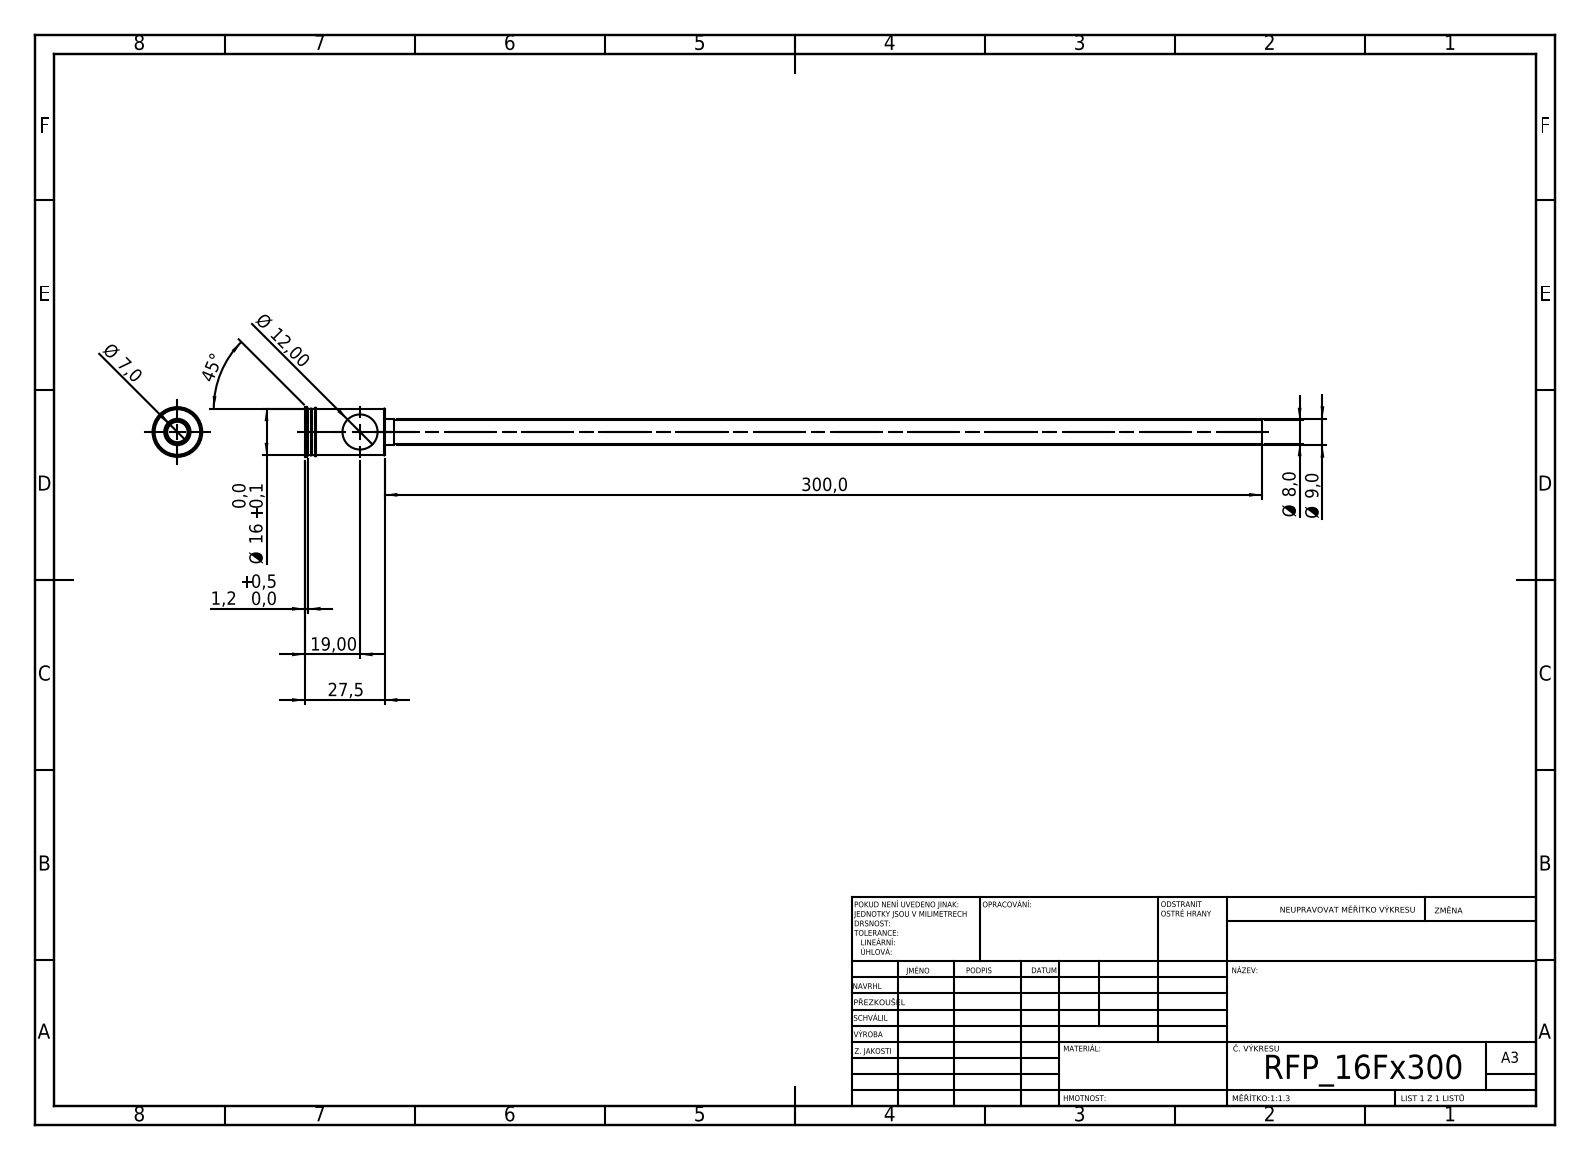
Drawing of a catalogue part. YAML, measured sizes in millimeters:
step_written_by: "SolidWorks 2019 (CONFIG_CONTROL_DESIGN)"
units: millimeters
bodies: {solids: 1, faces: 44, planar: 20, cylindrical: 16, other: 8}
overall_size: [327.5, 17, 17]
volume: 7127
surface_area: 16328
round_holes:
  - {diameter: 7, count: 1}
  - {diameter: 12, count: 1}
round_bosses_or_shafts:
  - {diameter: 17, count: 1}
  - {diameter: 16, count: 1}
  - {diameter: 9, count: 1}
  - {diameter: 8, count: 1}
face_to_face_distances: [25.5, 2, 27.5, 11.4, 0.5, 25, 2.5, 3, 28, 28.5]
